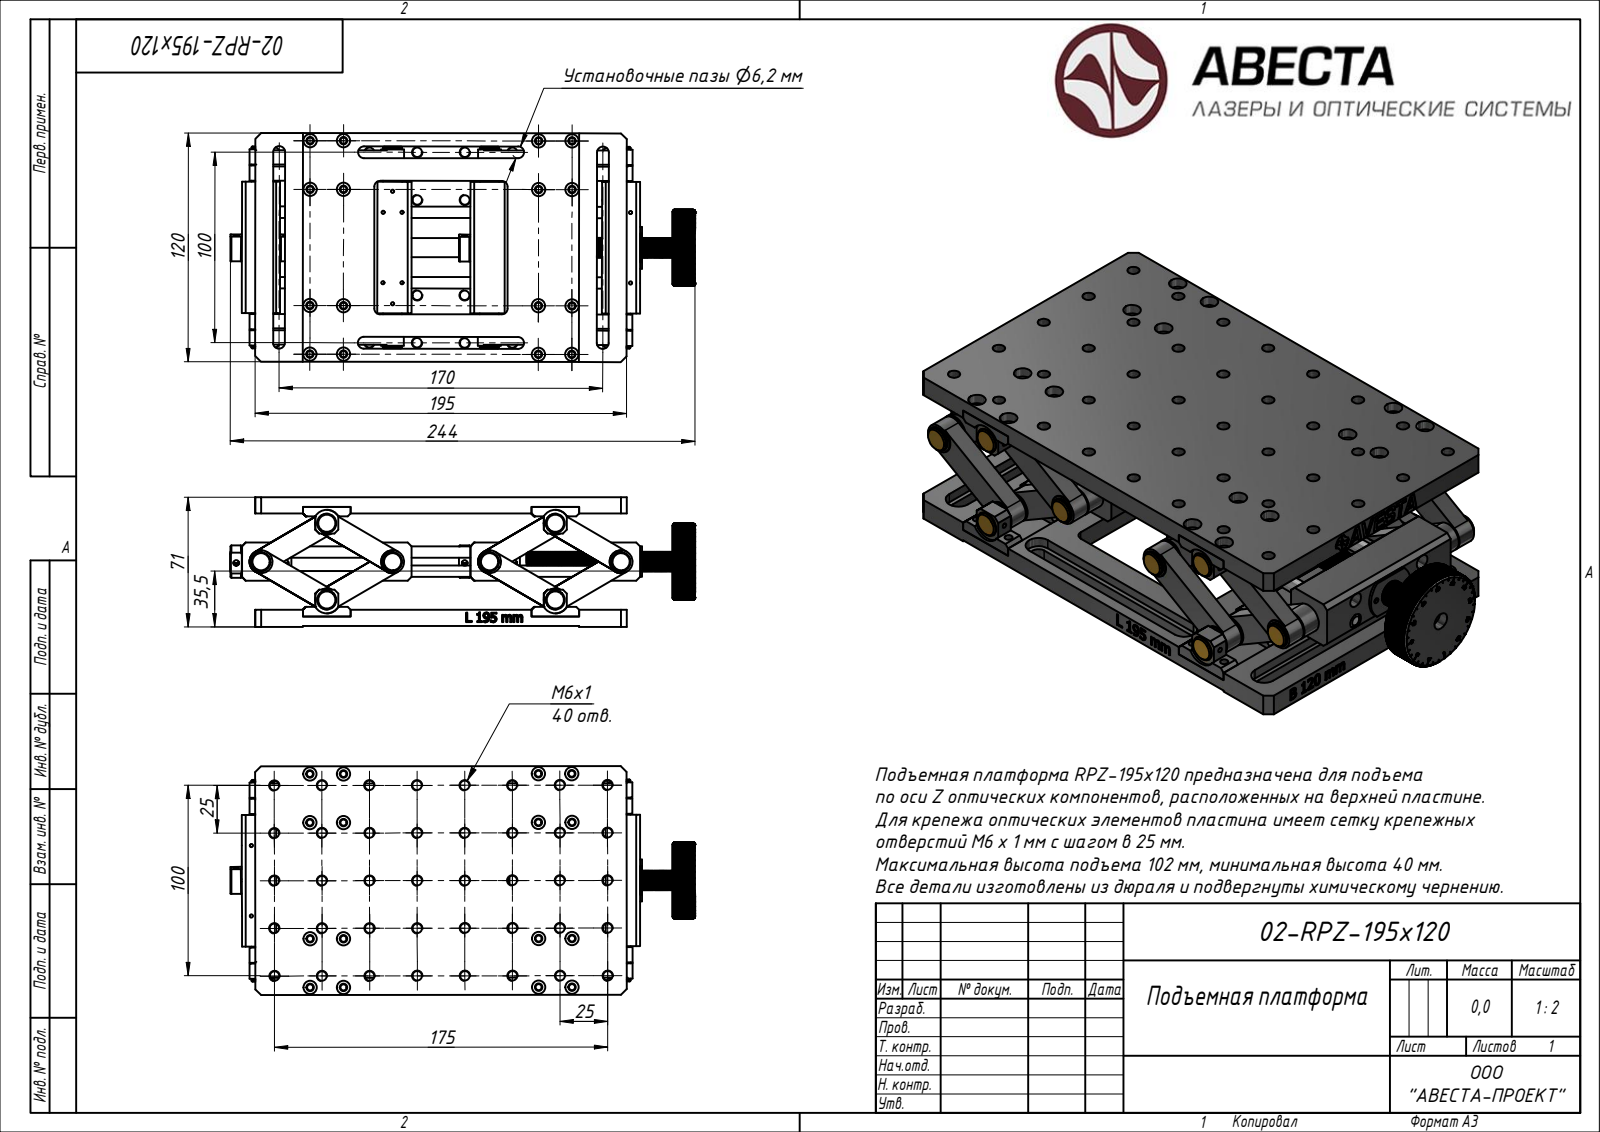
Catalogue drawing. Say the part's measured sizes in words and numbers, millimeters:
The part is named "Платформа 195х120 без подшипников; Платформа 195х120 без подшипников_Substitute_1". Its 3-D file was written by "Autodesk Inventor 2019 (AUTOMOTIVE_DESIGN)". It is 97 solids with 3843 faces: 2324 planar, 894 cylindrical and 625 other. Overall it measures 244.03 by 120.19 by 70.43 millimeters. Its volume is 547 796 cubic millimeters and its surface area 259 612 square millimeters. Round holes: 40 of diameter 4.9, 24 of diameter 2, 21 of diameter 4, 18 of diameter 1.6, 17 of diameter 7, 16 of diameter 3.24, 8 of diameter 1.57, 8 of diameter 3, 8 of diameter 5, 8 of diameter 8, 5 of diameter 3.2, 4 of diameter 6. Round bosses or shafts: 8 of diameter 12, 8 of diameter 10, 8 of diameter 4.02. Partial cylindrical surfaces (rounded edges, fillets, slot ends): 8 of radius 3.1, 8 of radius 5.1, 4 of radius 3, 4 of radius 7, 2 of radius 8.5, 1 of radius 6, 1 of radius 11, 1 of radius 19. The main face-to-face distances are 8.5, 5, 64.93, 56.43, 3.5, 61.43, 0.5, 59.93, 9, 94.5. The hole center spacings are 120, 10, 86.5, 17.6, 25.5, 187.63, 37, 38.33.
